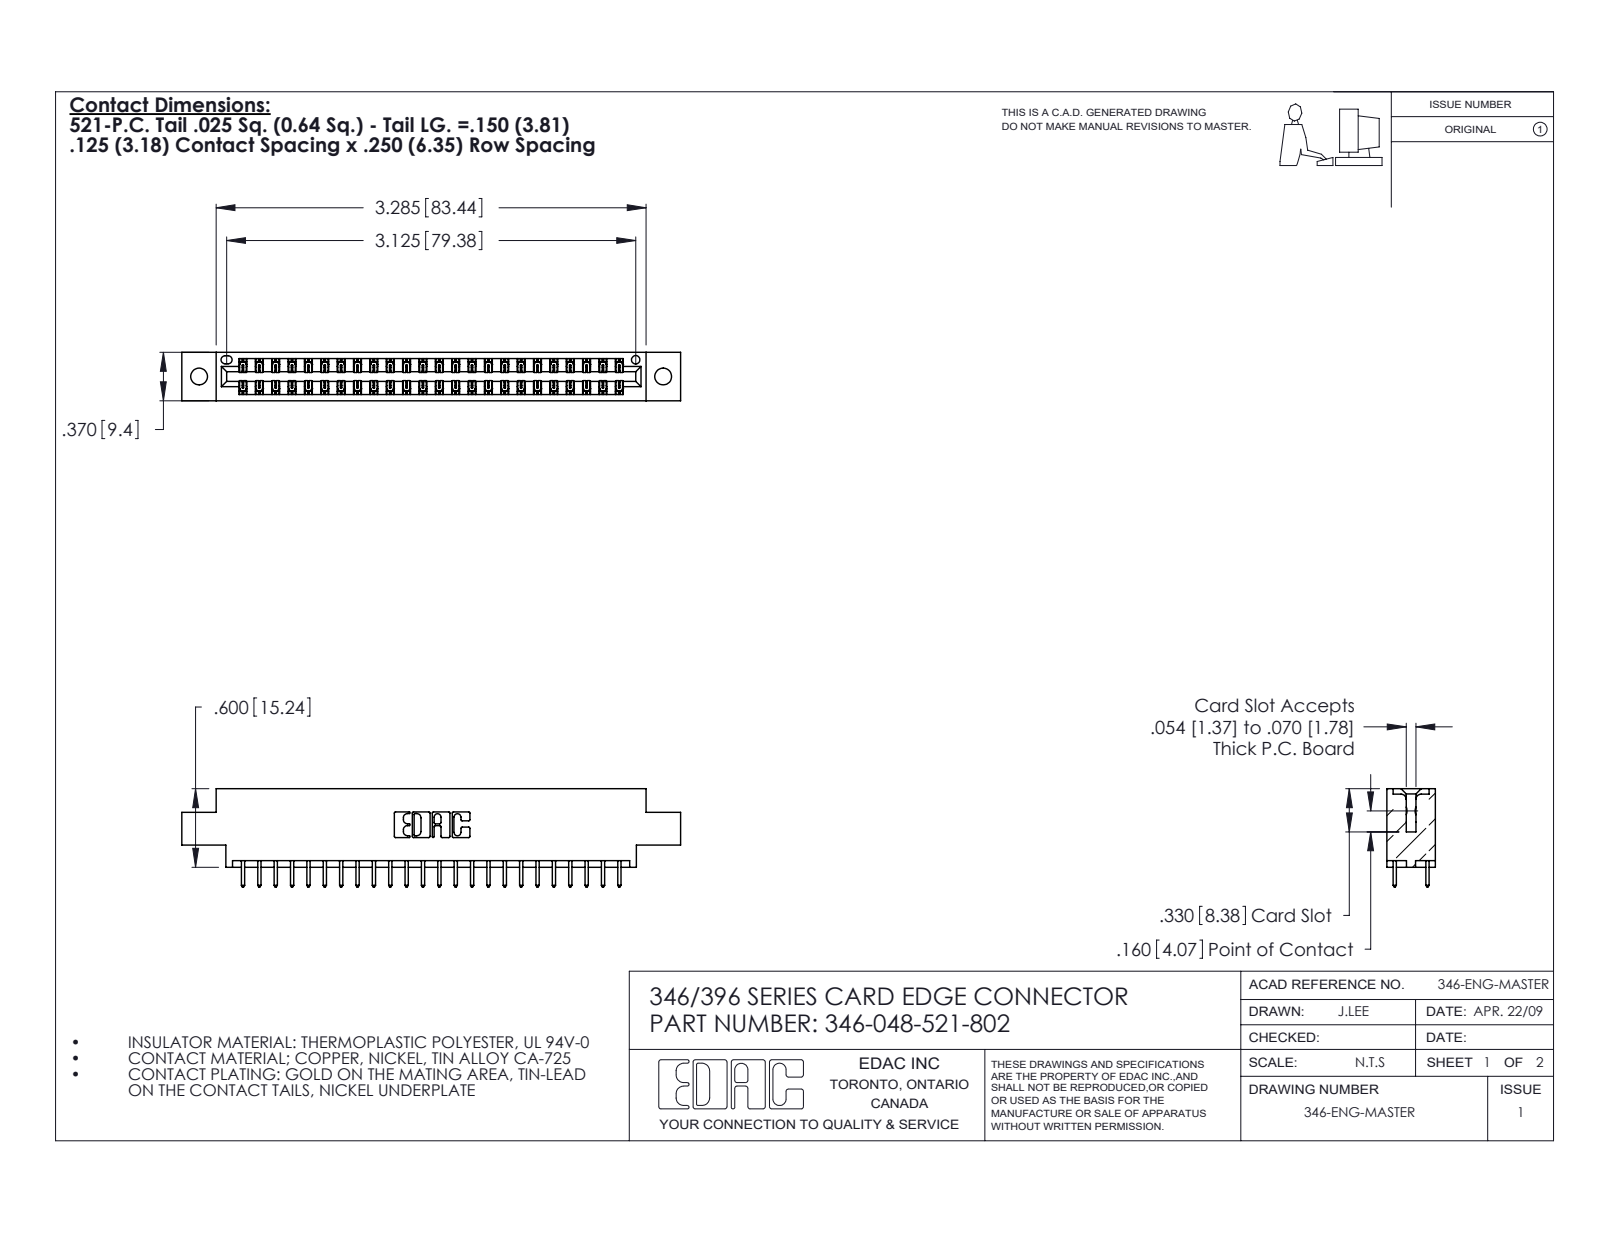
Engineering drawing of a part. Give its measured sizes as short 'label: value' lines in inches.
name: 345-292-001_345-293-121; 346 Part_0.170 Offset - 0.128 Dia; 346-048-521-802
written by: SolidWorks 2020 (CONFIG_CONTROL_DESIGN)
unit: in
bodies: 49 solids, 2622 faces (1760 planar, 862 cylindrical, 0 other)
size: 3.81 × 0.75 × 0.37
volume: 0.554 in³; area: 18.58 in²
holes: 2× ⌀0.128, 1× ⌀0.064
rounds: 72× R0.006, 48× R0.01, 22× R0.01, 6× R0.007, 6× R0.031, 3× R0.026, 2× R0.014, 2× R0.022
face distances: 0.048, 0.322, 0.37, 0.25, 0.072, 0.298, 0.025, 0.275, 0.148, 0.222
hole spacings: 0.246, 3.337, 3.545
